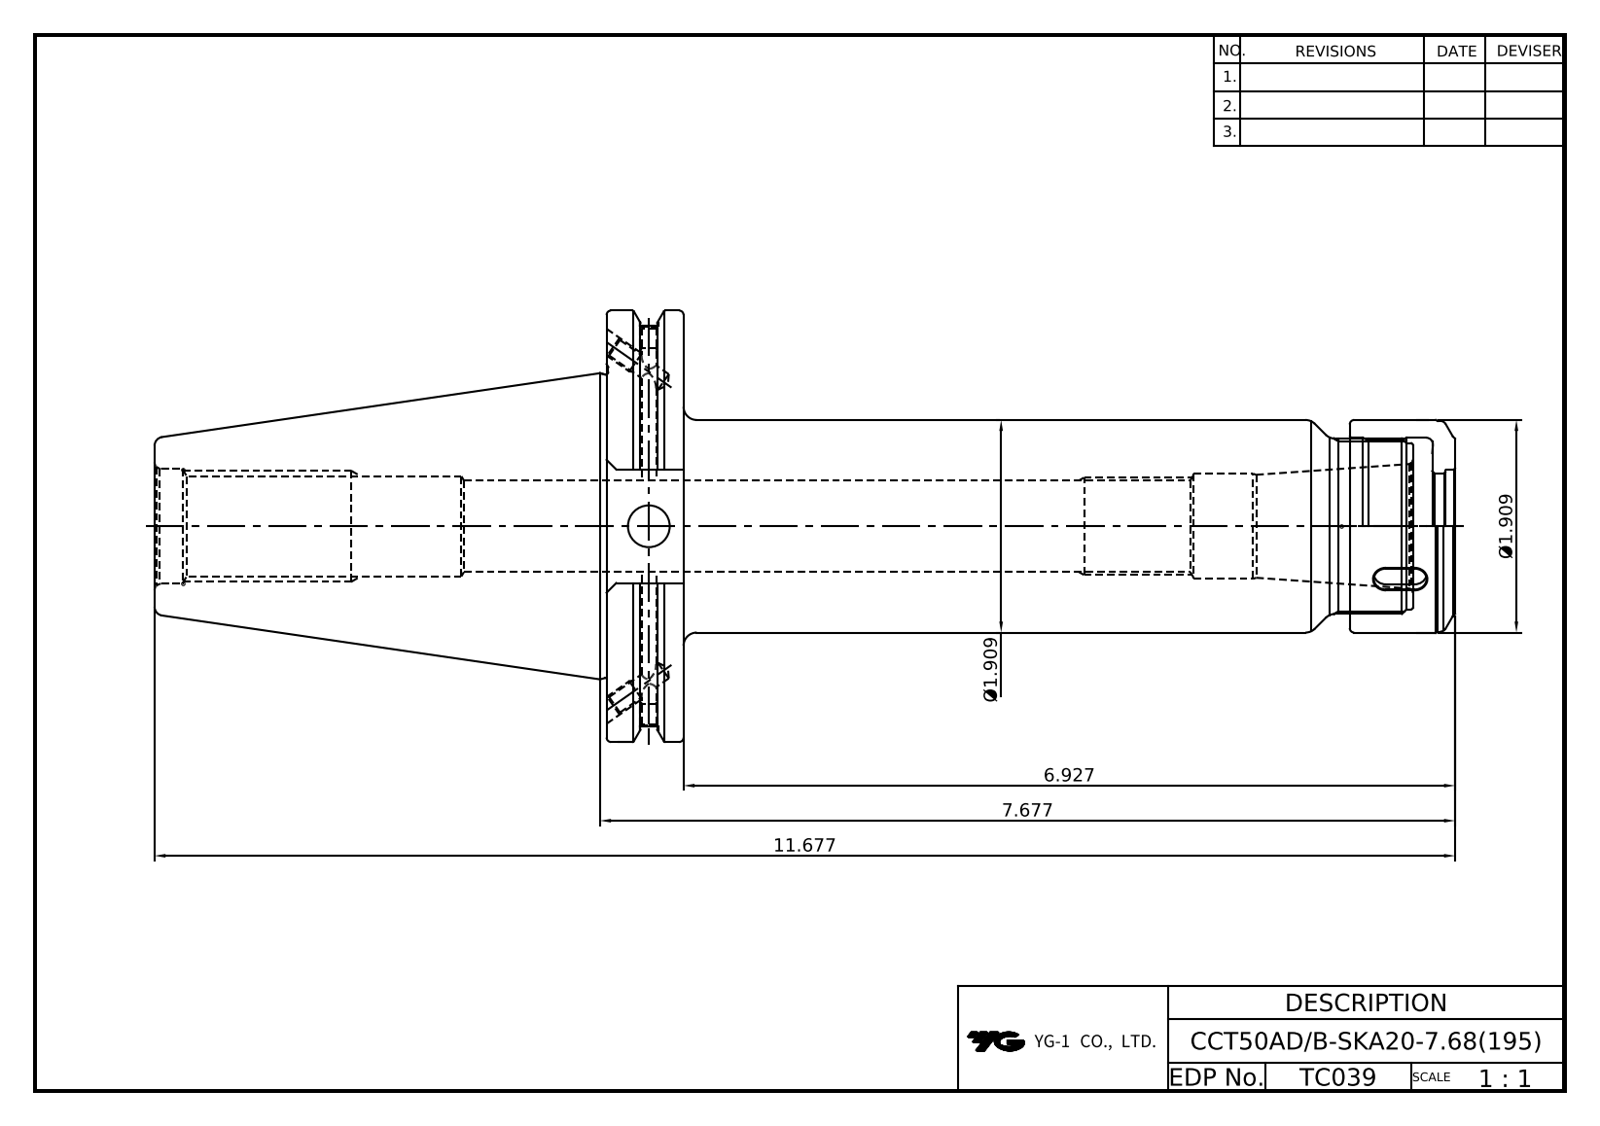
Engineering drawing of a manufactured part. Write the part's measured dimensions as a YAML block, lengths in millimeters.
part_name: "LO-CCT50ADB-SKA20-195; SKN20-NUT"
step_written_by: "Autodesk Inventor 2022 (AUTOMOTIVE_DESIGN)"
units: millimeters
bodies: {solids: 2, faces: 170, planar: 62, cylindrical: 46, other: 62}
overall_size: [296.6, 98.42, 94.69]
volume: 579480
surface_area: 88298
round_holes:
  - {diameter: 3.24, count: 2}
  - {diameter: 4.13, count: 2}
  - {diameter: 4.2, count: 2}
  - {diameter: 5, count: 2}
  - {diameter: 9.53, count: 1}
  - {diameter: 19.18, count: 1}
  - {diameter: 21.97, count: 1}
  - {diameter: 24, count: 1}
  - {diameter: 26.2, count: 1}
  - {diameter: 29.2, count: 1}
  - {diameter: 31, count: 1}
  - {diameter: 38.92, count: 1}
round_bosses_or_shafts:
  - {diameter: 98.42, count: 1}
  - {diameter: 91.29, count: 1}
  - {diameter: 69.25, count: 1}
  - {diameter: 48.5, count: 1}
  - {diameter: 48.1, count: 1}
  - {diameter: 40, count: 1}
  - {diameter: 38, count: 1}
face_to_face_distances: [17.55, 103.1, 120.65, 296.6, 193.5, 175.95, 73.03, 272.6, 169.5, 151.95]
